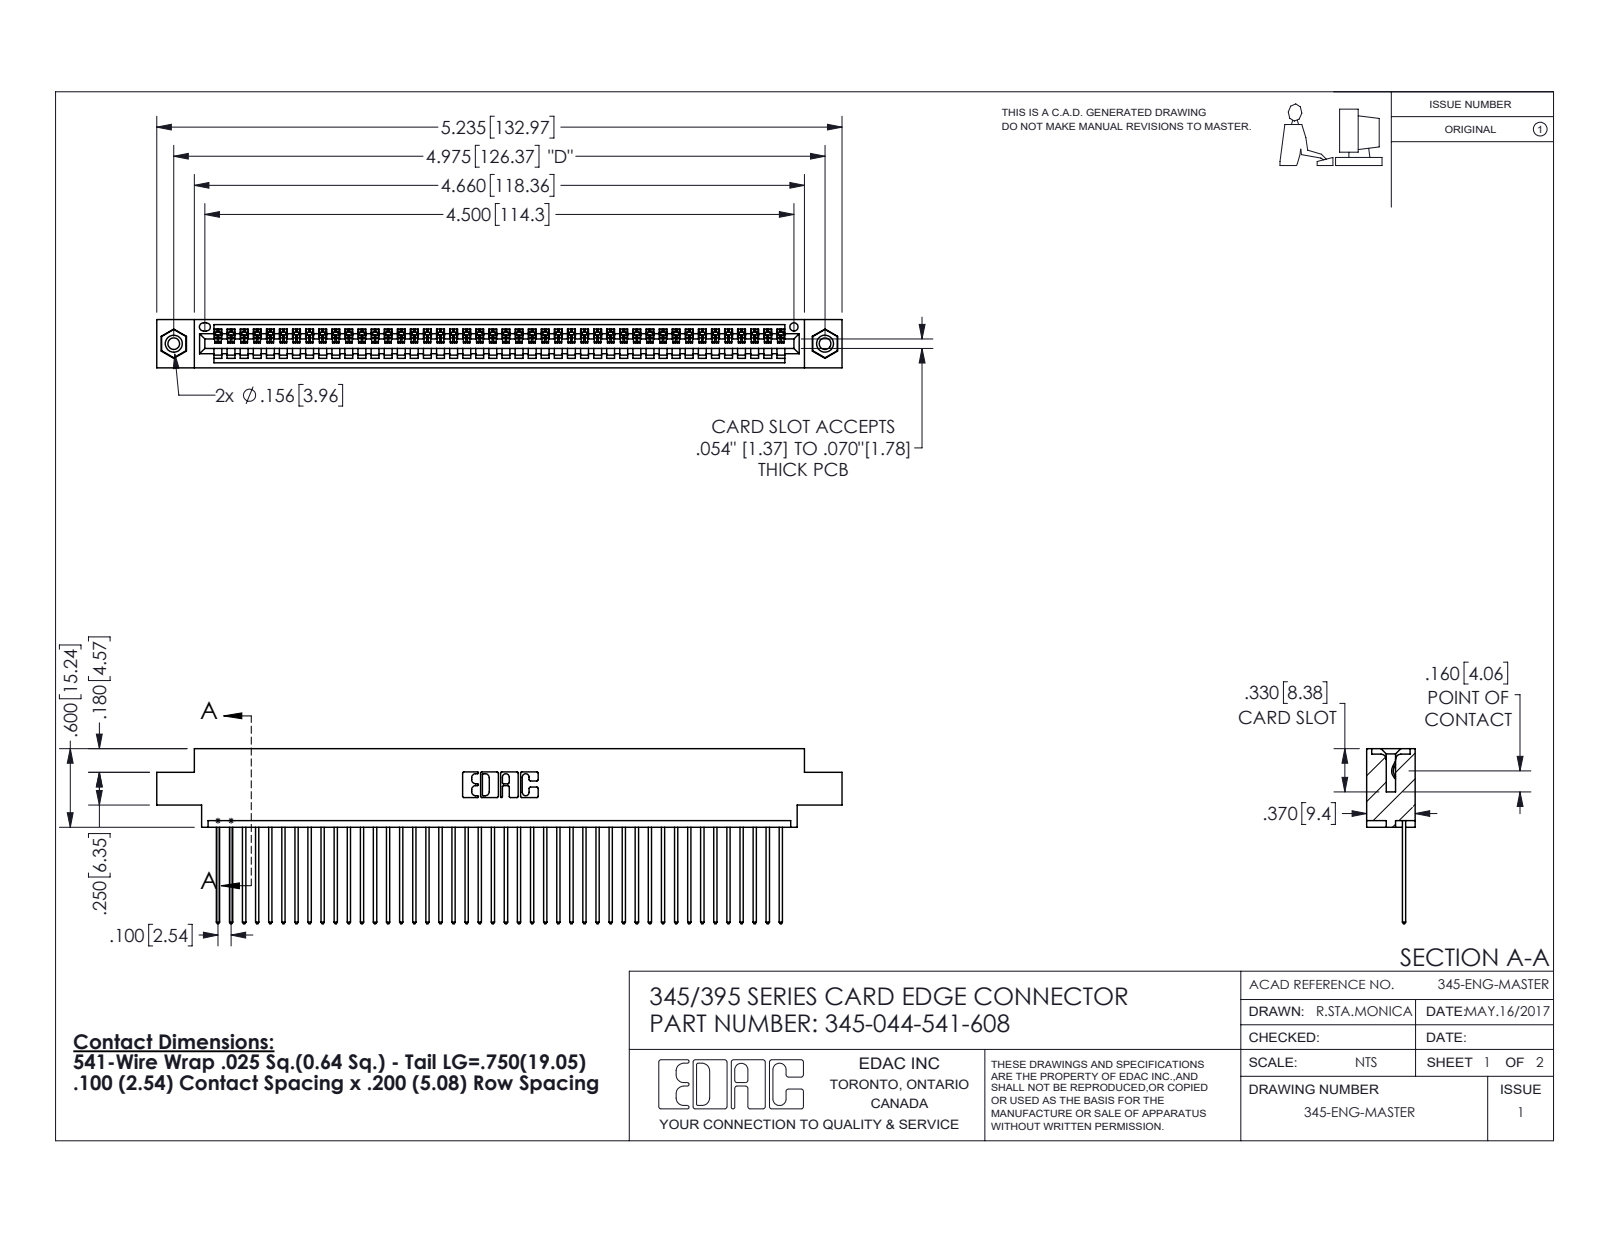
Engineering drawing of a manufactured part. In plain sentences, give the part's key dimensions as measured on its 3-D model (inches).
The part is named "345-044-541-608; 345-292-001_345-293-141; 345-250-001_345-250-003-102; 345 Part_0.170 Offset - 0.156 Dia-TI". Its 3-D file was written by "SolidWorks 2016 (CONFIG_CONTROL_DESIGN)". It is 47 solids with 2742 faces: 1876 planar, 850 cylindrical and 16 other. Overall it measures 5.235 by 1.337 by 0.37 inches. Its volume is 0.773 cubic inches and its surface area 27.69 square inches. Round holes: 2 of diameter 0.089, 2 of diameter 0.125, 2 of diameter 0.156, 1 of diameter 0.064. Round bosses or shafts: 2 of diameter 0.155. Partial cylindrical surfaces (rounded edges, fillets, slot ends): 88 of radius 0.006, 88 of radius 0.01, 22 of radius 0.01, 6 of radius 0.007, 6 of radius 0.031, 3 of radius 0.026, 2 of radius 0.031, 2 of radius 0.04. The main face-to-face distances are 0.072, 0.298, 0.37, 0.098, 0.272, 0.025, 0.2, 0.225, 0.175, 0.149. The hole center spacings are 0.27, 4.739, 4.975.
